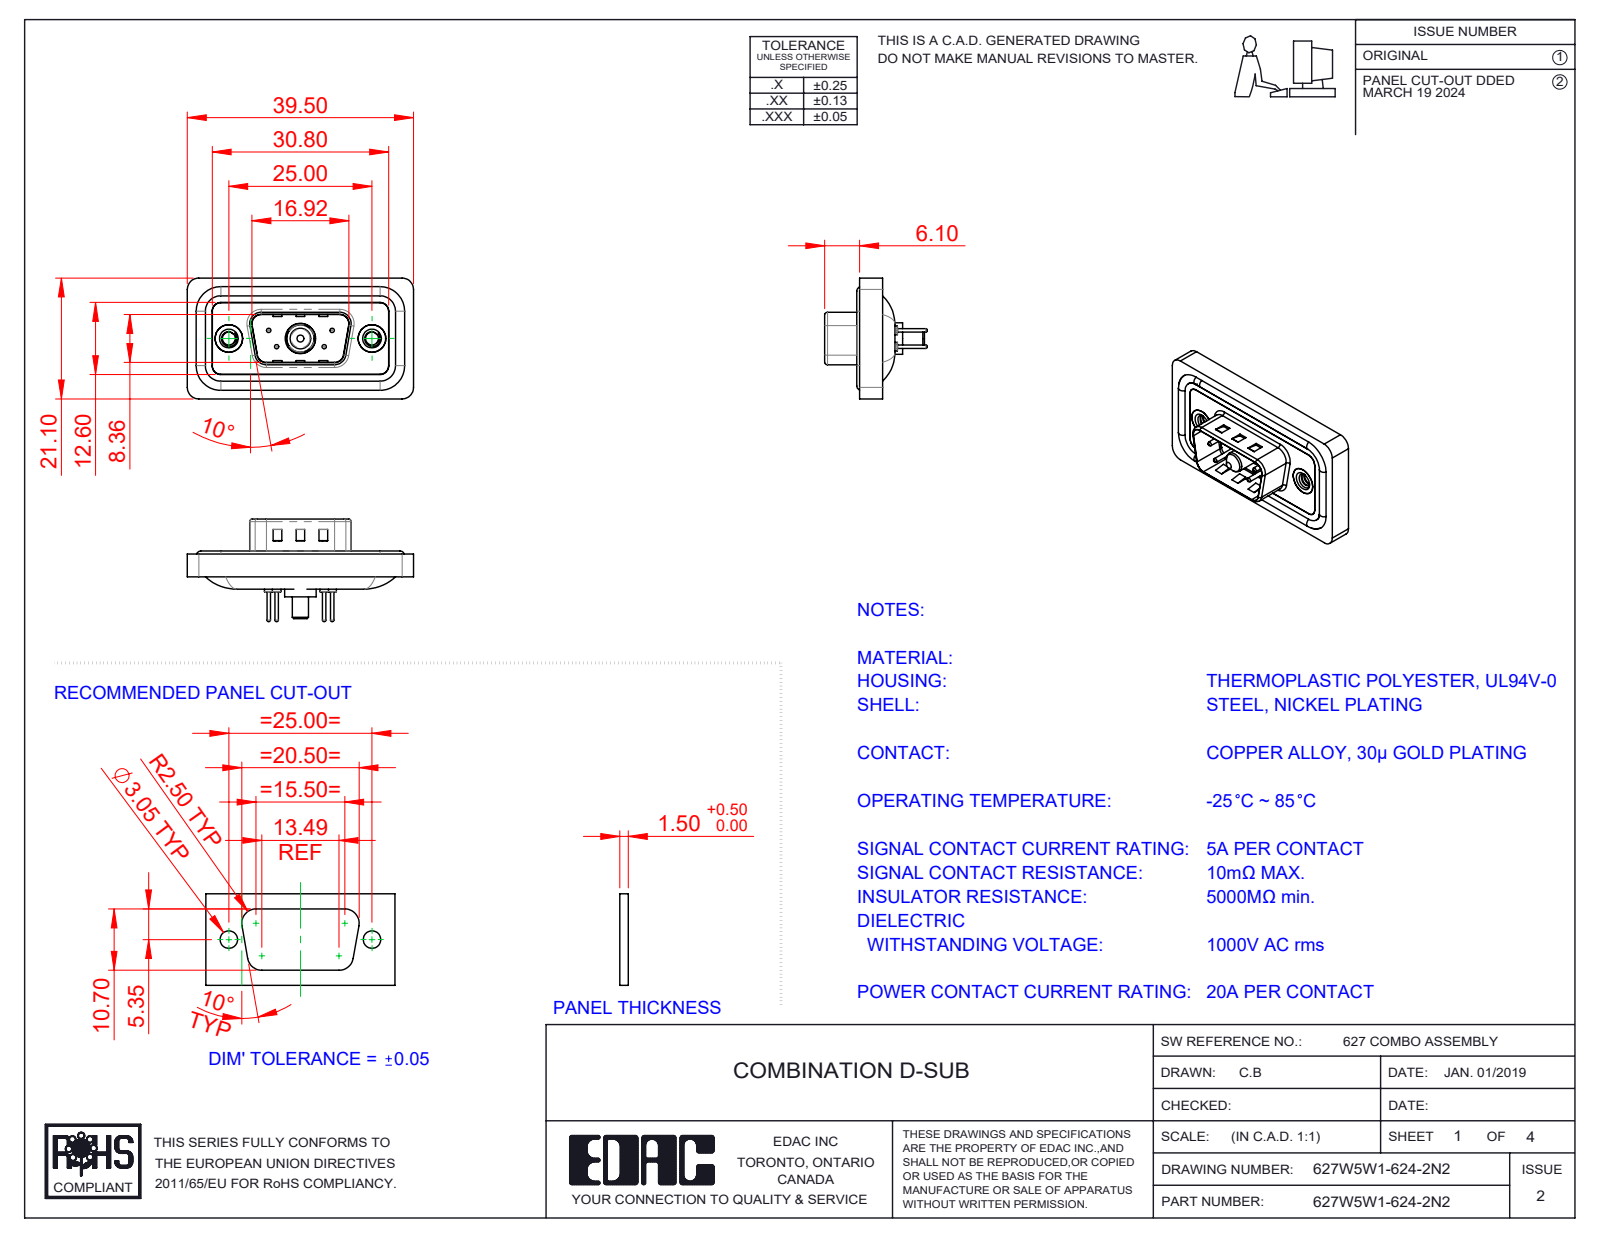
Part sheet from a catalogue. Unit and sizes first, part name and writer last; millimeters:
Units: millimetres
Overall size (bounding box): 39.5 × 21.1 × 17.9
Round holes (diameter × count): ⌀0.75 ×4, ⌀1.6 ×4, ⌀2 ×4, ⌀2.26 ×2, ⌀4 ×2, ⌀4.8 ×2, ⌀5 ×2, ⌀4.85 ×1, ⌀5.3 ×1
Round bosses / shafts (diameter × count): ⌀1.6 ×4, ⌀1.5 ×4, ⌀0.6 ×4, ⌀4.9 ×2, ⌀5.5 ×1, ⌀5.2 ×1, ⌀4.75 ×1, ⌀3.75 ×1
Partial cylindrical surfaces — rounded edges, fillets, slot ends (radius × count): R1.5 ×22, R2 ×18, R0.5 ×8, R1.6 ×8, R0.25 ×4, R0.6 ×4, R0.65 ×4, R0.9 ×4
Main face-to-face distances: 0.4, 1.1, 2.9, 1.6, 1.5, 3.1, 0.5, 2.5, 4, 0.8
Hole centre spacings: 3.16, 5.72, 7.1, 12.5, 18.1, 4.39, 4.4, 8.31
Volume: 4 388 mm³ · Surface area: 6 941 mm²
Bodies: 13 solids, 598 faces (183 planar, 255 cylindrical, 160 other)
Part name (STEP PRODUCT): 627Combo Shell Front_09 Contacts; 627W5W1-624-2N2; 627Combo Threaded Rivet_2; 627Combo Contact Row 1_24 (+5 more)
STEP written by: SolidWorks 2023 (CONFIG_CONTROL_DESIGN)
